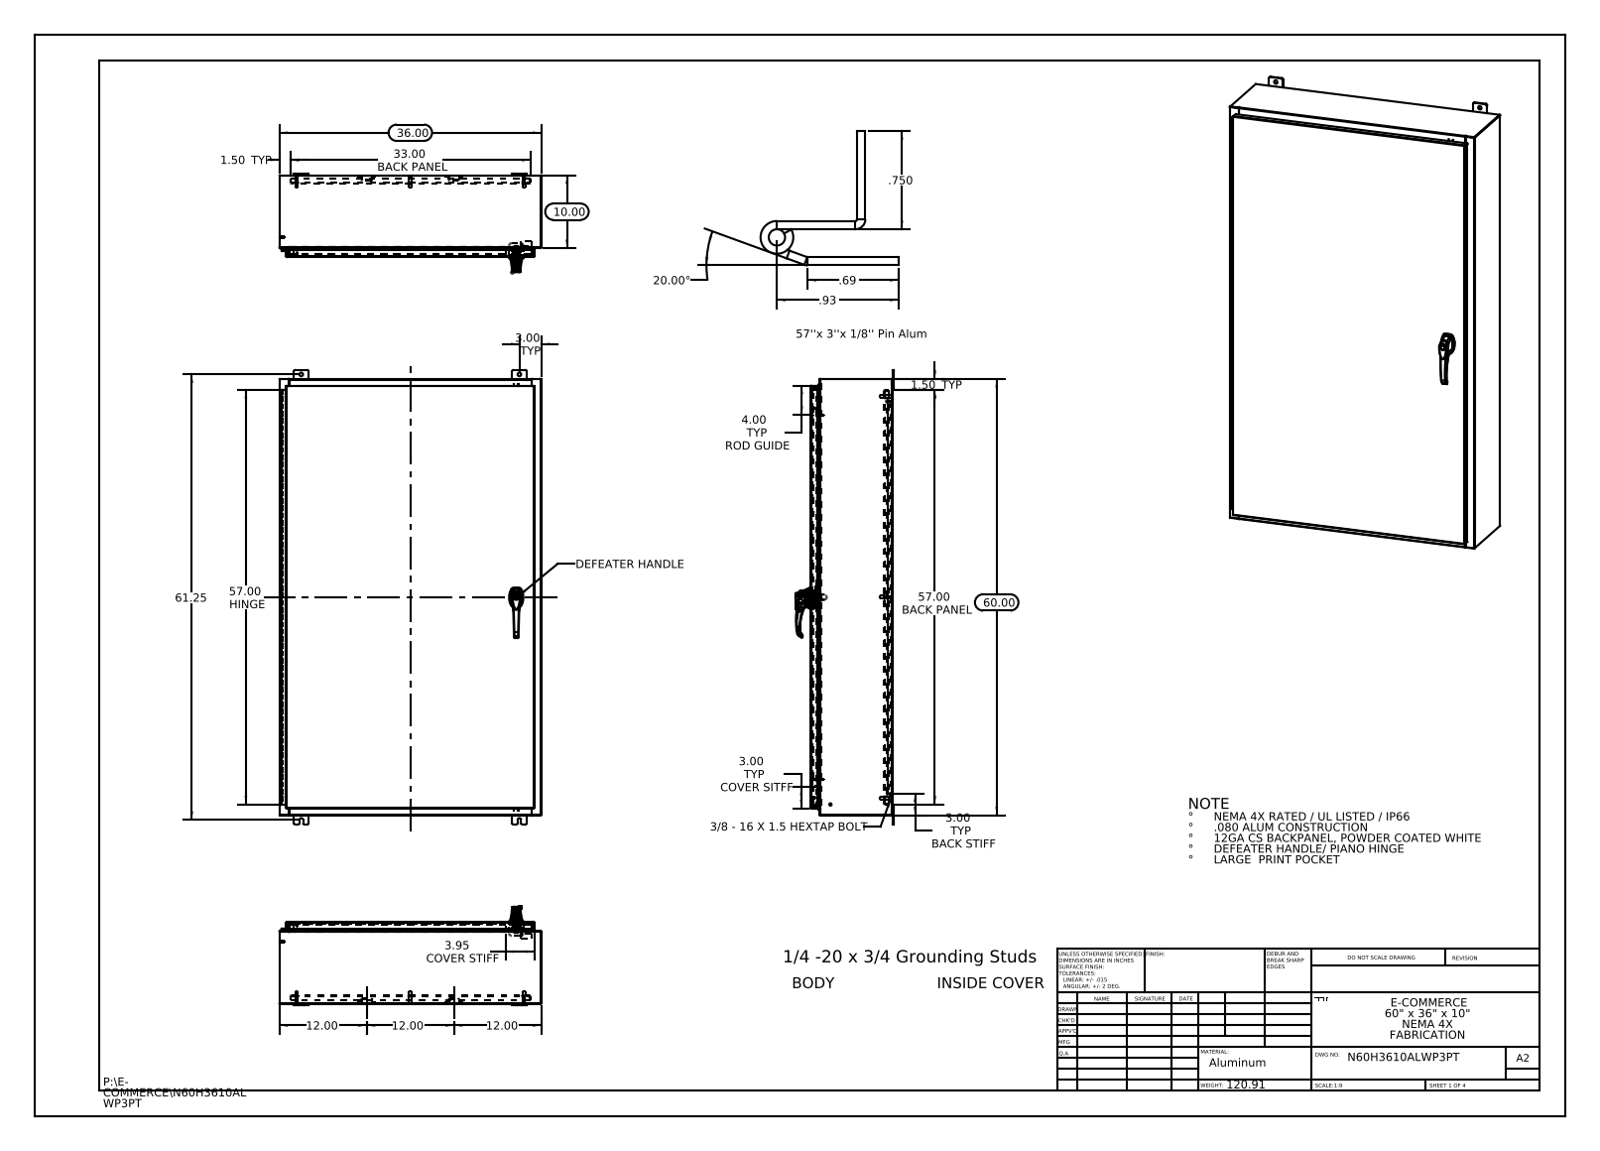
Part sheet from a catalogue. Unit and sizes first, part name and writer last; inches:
Units: inches
Overall size (bounding box): 62.5 × 36 × 13.495
Round holes (diameter × count): ⌀0.5 ×12, ⌀0.25 ×10, ⌀0.138 ×3, ⌀0.161 ×3, ⌀0.079 ×2, ⌀0.203 ×2, ⌀0.313 ×2, ⌀0.437 ×2, ⌀0.125 ×1, ⌀0.125 ×1, ⌀0.197 ×1, ⌀0.276 ×1
Round bosses / shafts (diameter × count): ⌀0.157 ×10, ⌀0.14 ×10, ⌀0.625 ×8, ⌀0.375 ×8, ⌀0.33 ×8, ⌀0.315 ×3, ⌀0.236 ×3, ⌀1.181 ×1
Partial cylindrical surfaces — rounded edges, fillets, slot ends (radius × count): R0.118 ×37, R0.013 ×34, R0.006 ×33, R0.088 ×28, R0.19 ×24, R0.039 ×15, R0.028 ×12, R0.008 ×6
Main face-to-face distances: 0.075, 11.126, 11.051, 0.104, 11.201, 1, 10.126, 1.075, 10.051, 1.179
Hole centre spacings: 23.354, 25.662, 27.625, 41.709, 57.417, 30.975, 31.25, 55.25
Volume: 769.9 in³ · Surface area: 19 057 in²
Bodies: 51 solids, 3688 faces (1453 planar, 1449 cylindrical, 786 other)
Part name (STEP PRODUCT): N60H3610ALWP3PT 125 Pin Hinge; 10_30 CD Stud; N60H3610ALWP3PT Hinge Cover Side; 00005310_26163101 (+8 more)
STEP written by: SolidWorks 2013 (CONFIG_CONTROL_DESIGN)
